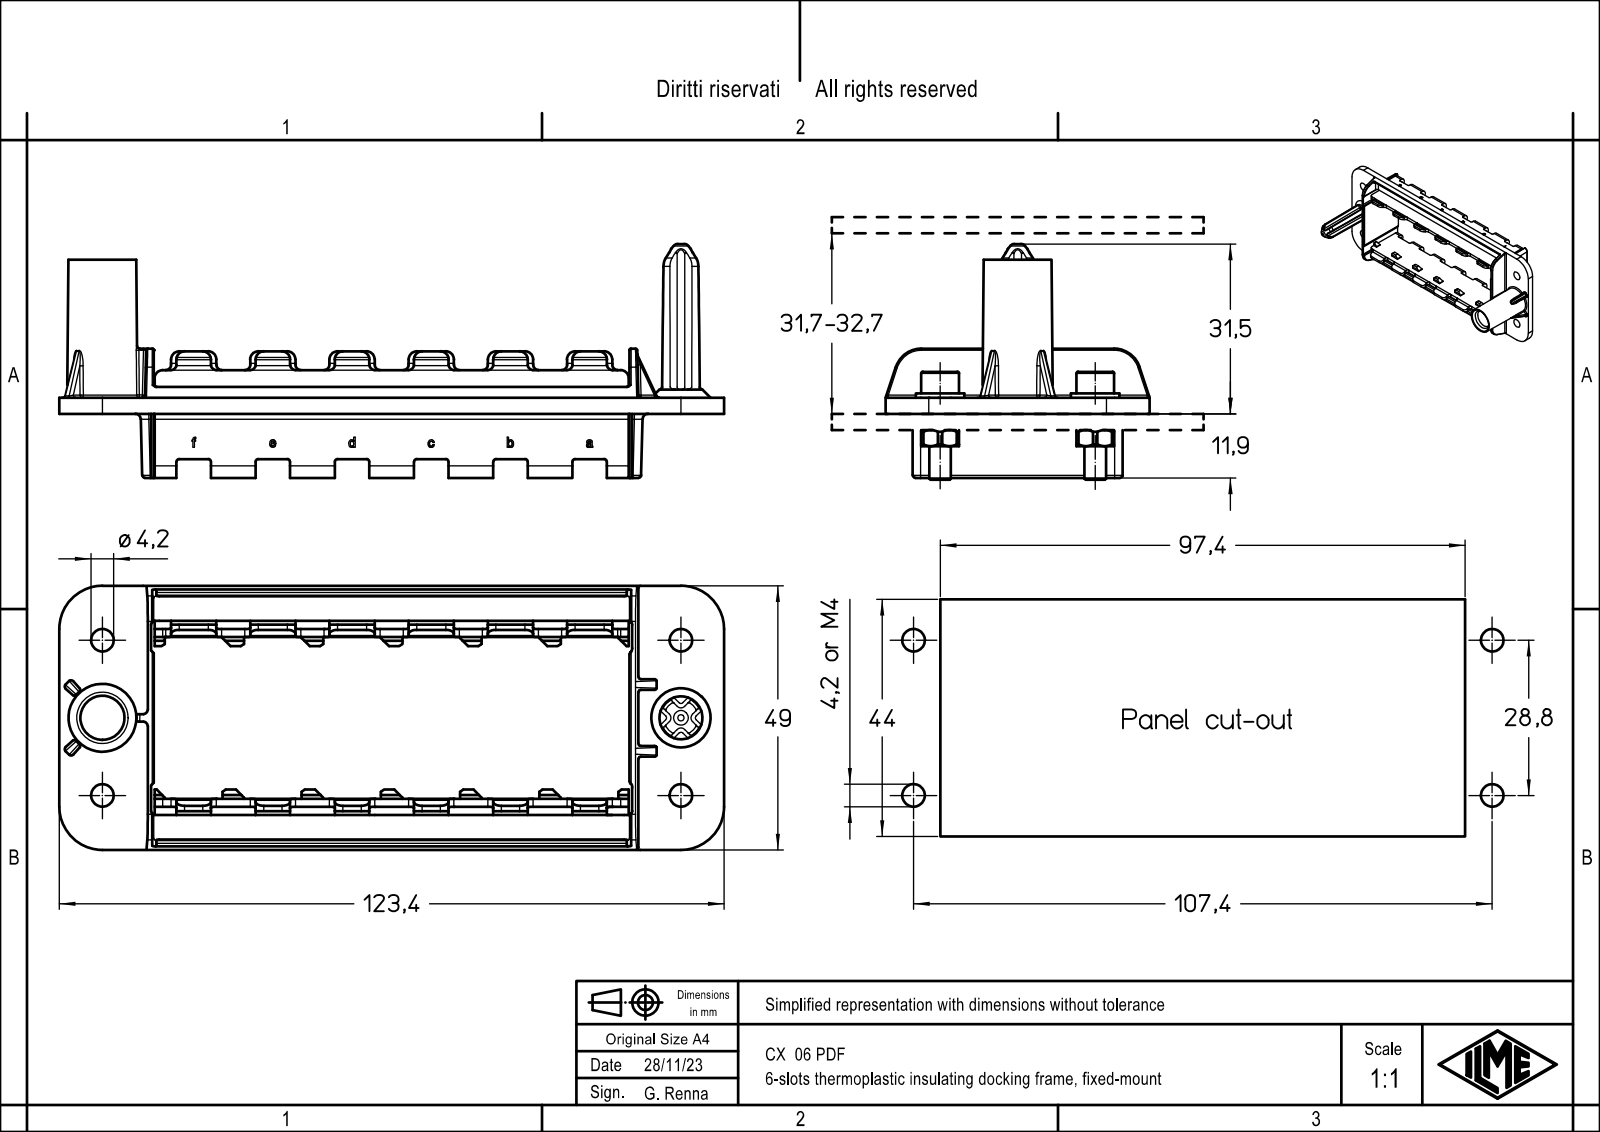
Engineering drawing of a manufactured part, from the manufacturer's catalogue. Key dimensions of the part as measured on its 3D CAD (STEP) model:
Part name (STEP PRODUCT): CX 06 PDF
STEP written by: Creo Elements/Direct Modeling 20.1B 02-Apr-2019 (C) Parametric Technology GmbH (AUTOMOTIVE_DESIGN)
Units: millimetres
Bodies: 1 solid, 596 faces (369 planar, 207 cylindrical, 20 other)
Overall size (bounding box): 123.4 × 49 × 43.4
Volume: 22 555 mm³ · Surface area: 25 566 mm²
Round holes (diameter × count): ⌀4.2 ×4
Partial cylindrical surfaces — rounded edges, fillets, slot ends (radius × count): R1 ×30, R1.5 ×30, R0.5 ×24, R0.1 ×15, R8 ×4, R0.75 ×2, R2 ×2, R2.25 ×2
Main face-to-face distances: 1.5, 3, 34.5, 33, 31.5, 36, 4.5, 37.5, 30, 5
Hole centre spacings: 28.8, 107.4, 111.19
